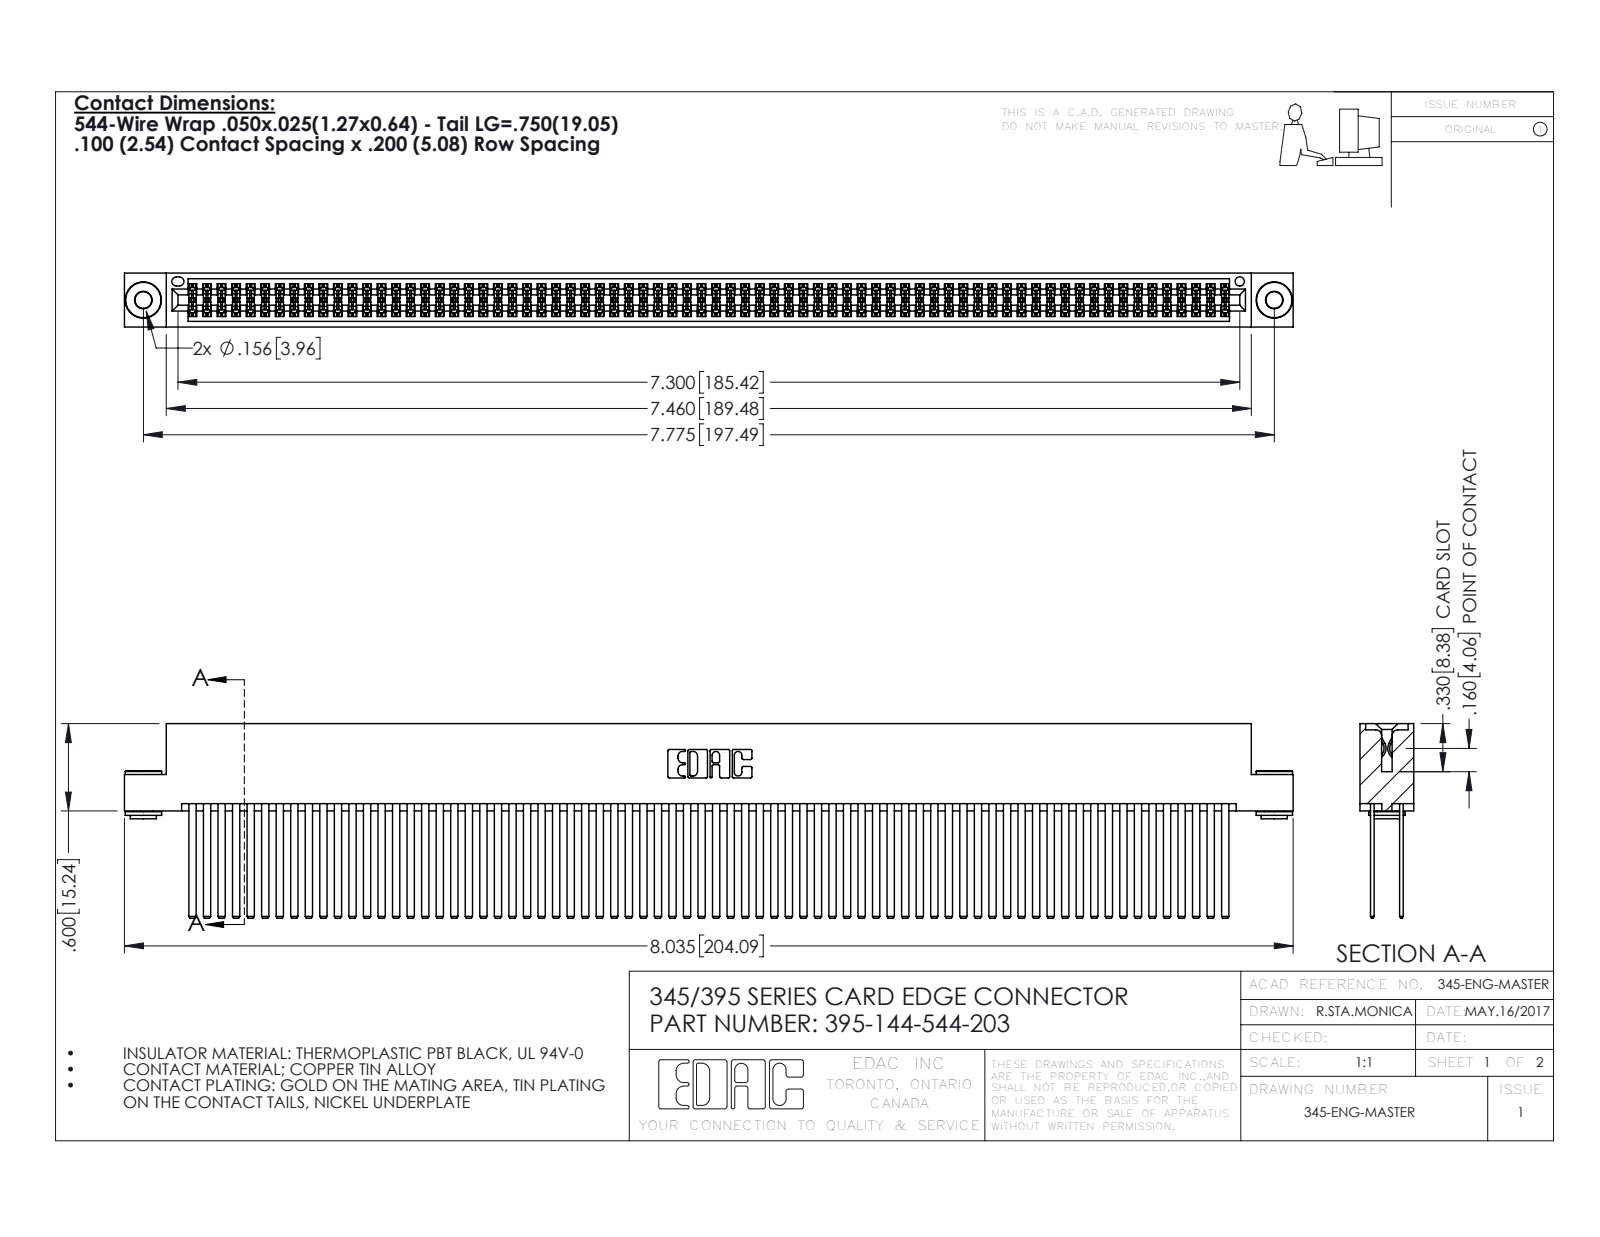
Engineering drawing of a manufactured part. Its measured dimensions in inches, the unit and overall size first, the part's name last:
Units: inches
Overall size (bounding box): 8.035 × 1.337 × 0.37
Round holes (diameter × count): ⌀0.116 ×2, ⌀0.156 ×2, ⌀0.064 ×1
Round bosses / shafts (diameter × count): ⌀0.25 ×2, ⌀0.18 ×2, ⌀0.136 ×2
Partial cylindrical surfaces — rounded edges, fillets, slot ends (radius × count): R0.006 ×216, R0.01 ×22, R0.007 ×6, R0.031 ×6, R0.026 ×3, R0.014 ×2, R0.019 ×2, R0.022 ×2
Main face-to-face distances: 0.2, 0.025, 0.072, 0.098, 0.272, 0.298, 0.225, 0.175, 0.37, 0.05
Hole centre spacings: 0.27, 7.539, 7.775
Volume: 1.351 in³ · Surface area: 61.12 in²
Bodies: 147 solids, 6500 faces (4266 planar, 2226 cylindrical, 8 other)
Part name (STEP PRODUCT): 345 Part_Flush Mounting Lugs - 0.156 Dia-TH; 345-250-002_345-250-002-102; 345-292-001_345-293-144; 395-144-544-203
STEP written by: SolidWorks 2016 (CONFIG_CONTROL_DESIGN)
